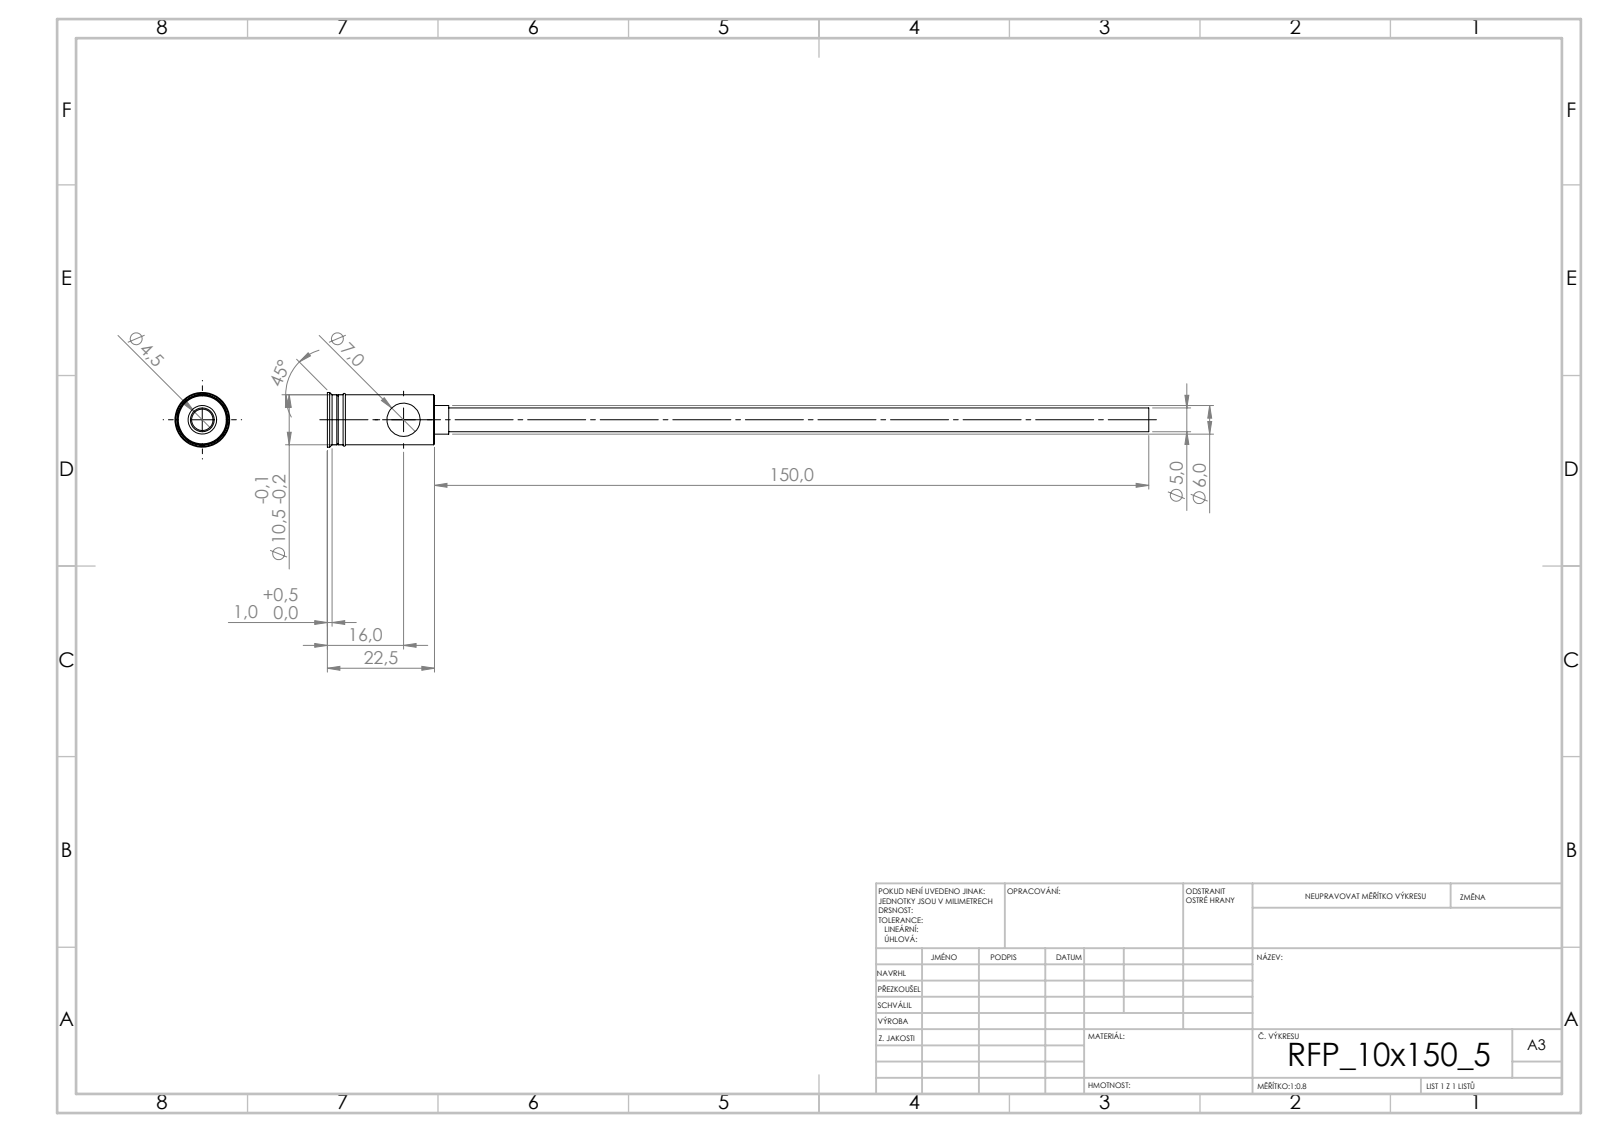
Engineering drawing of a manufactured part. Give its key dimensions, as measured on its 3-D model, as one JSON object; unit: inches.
{"step_written_by": "SolidWorks 2019 (CONFIG_CONTROL_DESIGN)", "units": "inches", "bodies": {"solids": 1, "faces": 44, "planar": 20, "cylindrical": 16, "other": 8}, "overall_size": [6.791, 0.453, 0.453], "volume_in3": 0.126, "surface_area_in2": 8.72, "round_holes": [[0.177, 1], [0.276, 1]], "round_bosses_or_shafts": [[0.453, 1], [0.413, 1], [0.236, 1], [0.197, 1]], "face_to_face_distances": [0.886, 0.807, 0.079, 0.232, 0.795, 0.091, 0.118, 0.913, 0.925, 1.004]}
